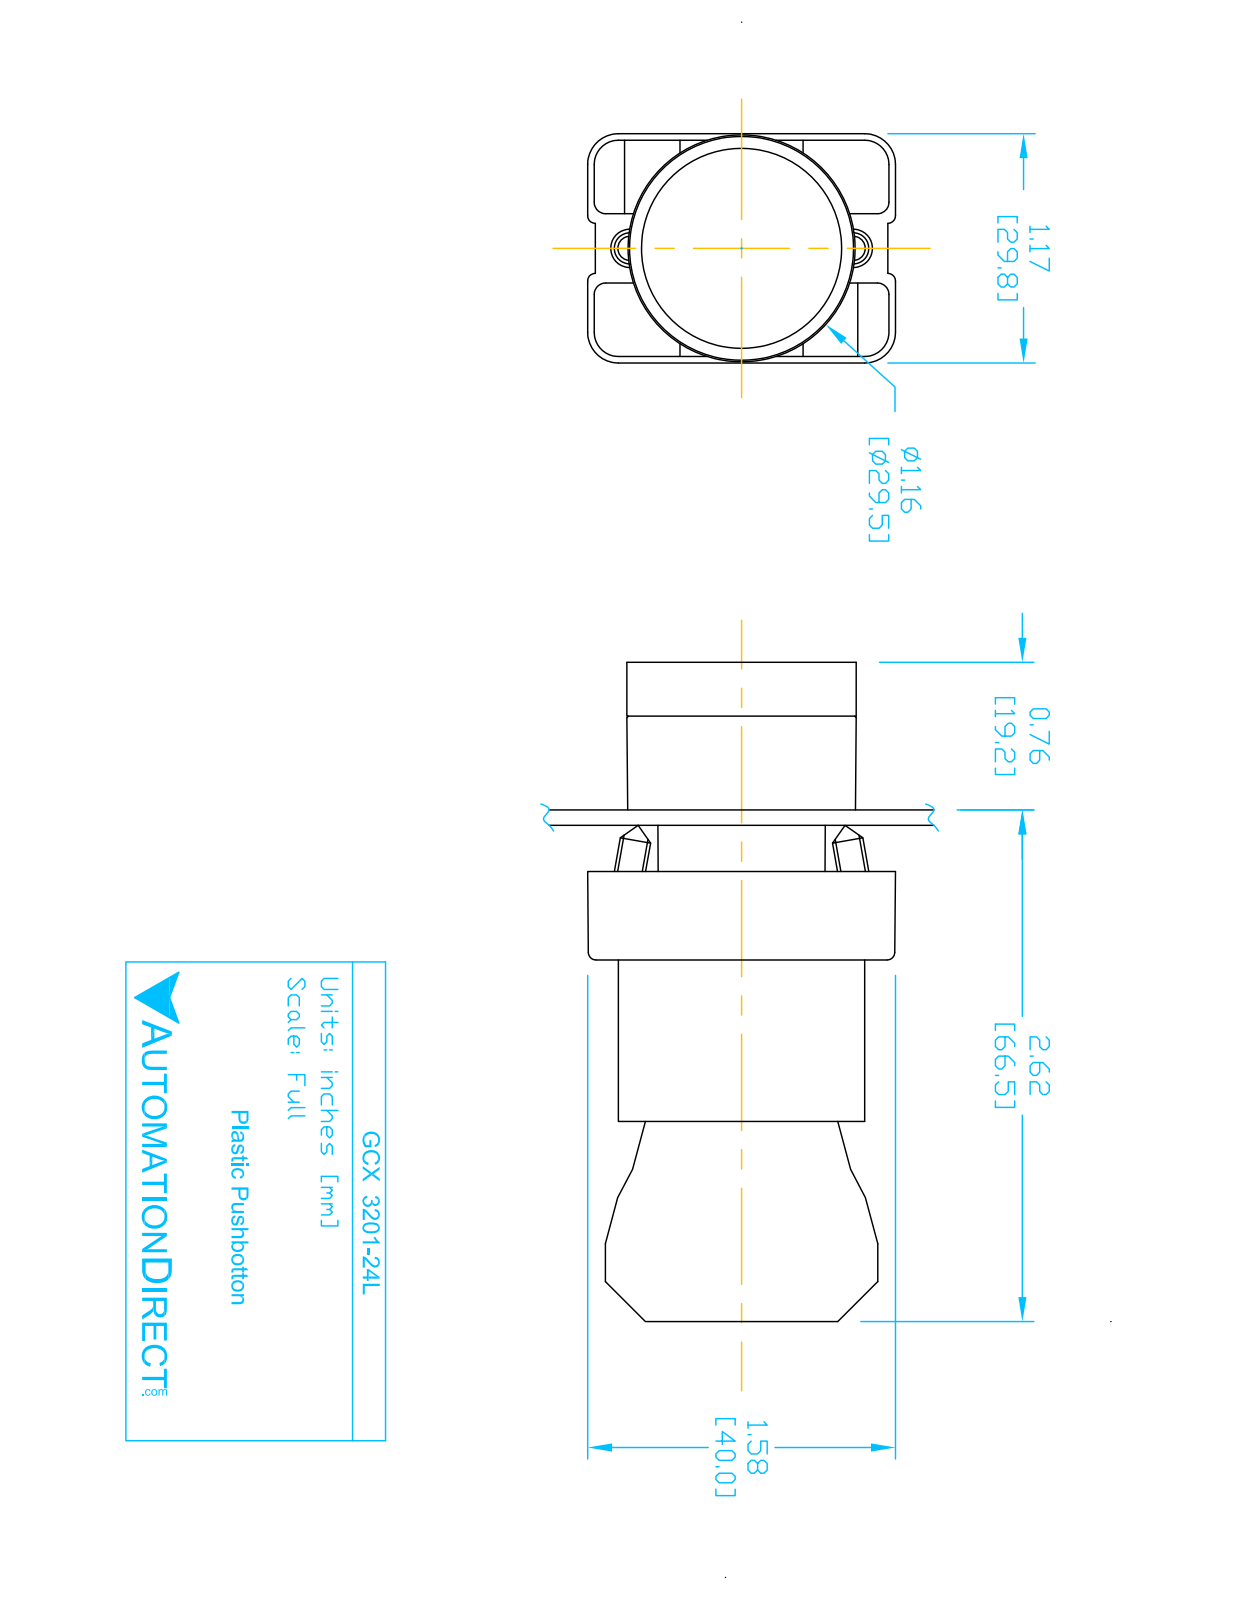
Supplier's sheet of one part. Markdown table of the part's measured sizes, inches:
| quantity | value |
| --- | --- |
| part name | ECX3029-2; GCX3201L OPERATOR; ECX1050; ecx1030 (+1 more) |
| STEP written by | SolidWorks 2016 (AUTOMOTIVE_DESIGN) |
| units | inches |
| bodies | 8 solids, 431 faces (252 planar, 148 cylindrical, 31 other) |
| overall size | 3.319 × 1.581 × 1.177 |
| volume | 2.794 in³ |
| surface area | 38.77 in² |
| round holes (diameter × count) | 0.079 × 2, 0.124 × 2, 0.13 × 2, 0.087 × 1, 0.197 × 1, 0.469 × 1, 0.878 × 1, 0.888 × 1, 1.024 × 1 |
| round bosses / shafts (diameter × count) | 0.157 × 4, 1.175 × 1, 1.004 × 1, 0.945 × 1, 0.856 × 1, 0.78 × 1, 0.504 × 1 |
| partial cylindrical surfaces (radius × count) | 0.059 × 24, 0.041 × 12, 0.124 × 12, 0.157 × 12, 0.039 × 8, 0.128 × 2, 0.02 × 1, 0.063 × 1 |
| main face-to-face distances | 0.827, 0.579, 2.02, 1.193, 1.171, 0.276, 2.295, 1.469, 0.031, 0.033 |
| hole center spacings | 0.236, 0.544, 0.472, 0.49 |
